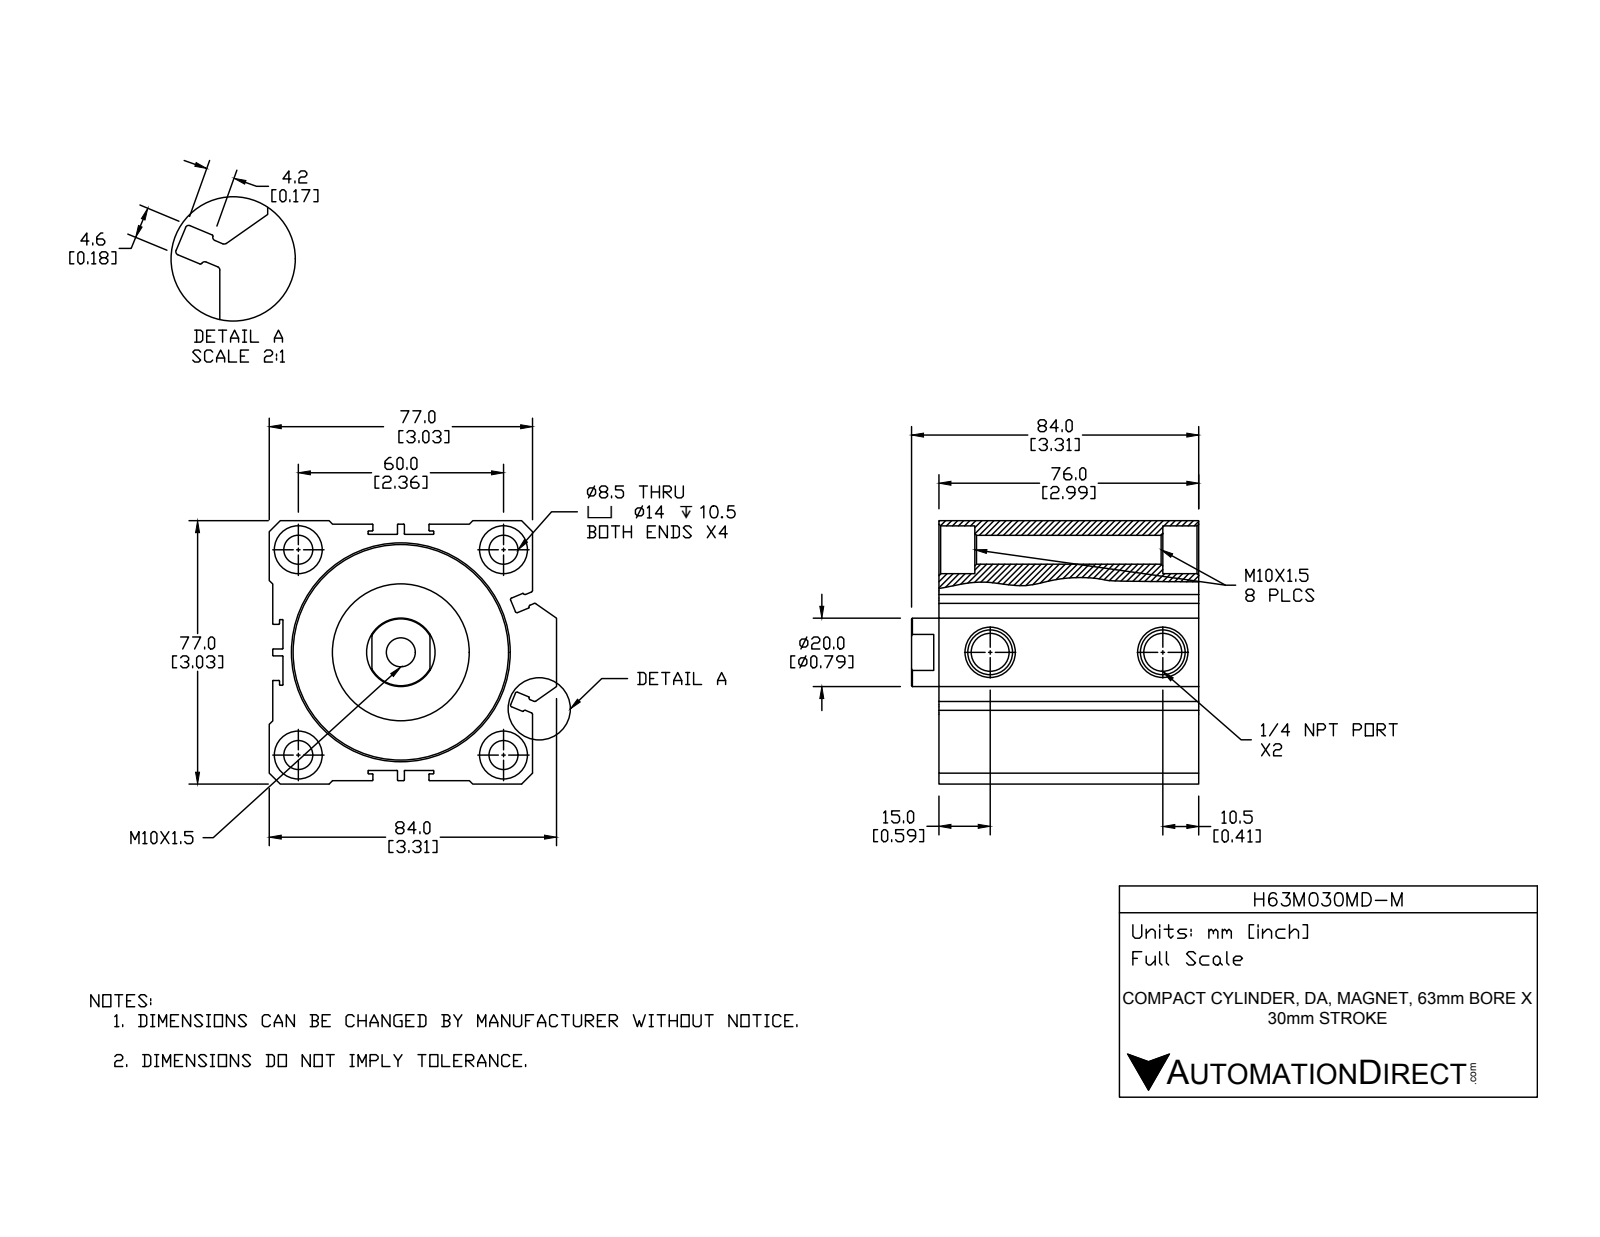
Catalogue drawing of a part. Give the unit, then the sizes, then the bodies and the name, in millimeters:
Units: millimetres
Overall size (bounding box): 84 × 84 × 77
Round holes (diameter × count): ⌀8.5 ×5, ⌀14 ×4, ⌀11.13 ×2, ⌀20 ×1, ⌀45.51 ×1, ⌀63 ×1
Round bosses / shafts (diameter × count): ⌀40 ×1, ⌀39 ×1
Partial cylindrical surfaces — rounded edges, fillets, slot ends (radius × count): R0.2 ×40, R0.5 ×12
Main face-to-face distances: 76, 1, 30.5, 3, 77, 4, 73, 23, 53.5, 2
Hole centre spacings: 42.43, 60, 84.85, 50.5
Volume: 308 554 mm³ · Surface area: 84 770 mm²
Bodies: 2 solids, 255 faces (99 planar, 103 cylindrical, 53 other)
Part name (STEP PRODUCT): H63M030MD-M-BODY; H63M030MD-M-PISTON; H63M030MD-M
STEP written by: SolidWorks 2015 (CONFIG_CONTROL_DESIGN)
